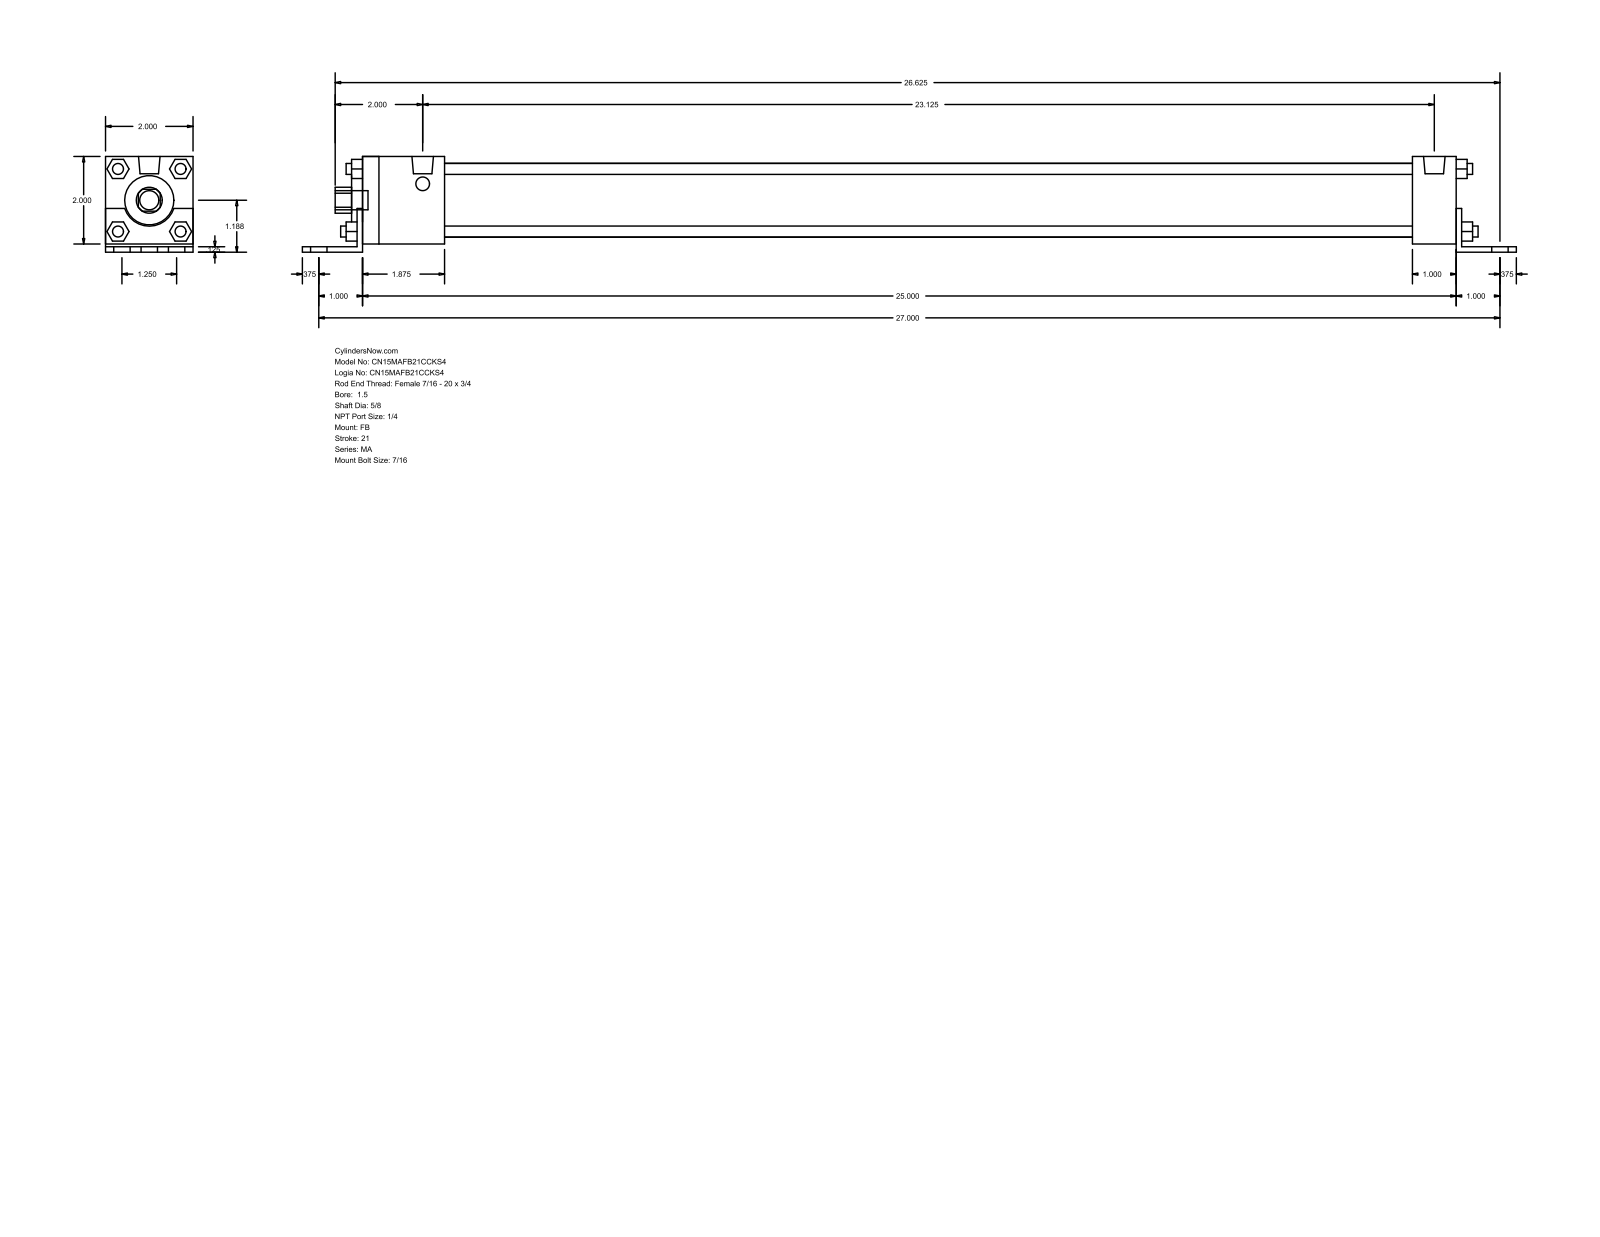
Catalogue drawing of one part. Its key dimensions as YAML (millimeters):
part_name: "MA_FB__0150_0.625"
step_written_by: "GSSL Pune (CONFIG_CONTROL_DESIGN)"
units: millimeters
bodies: {solids: 0, faces: 140, planar: 105, cylindrical: 35, other: 0}
overall_size: [704.85, 55.56, 50.8]
round_holes:
  - {diameter: 15.88, count: 1}
  - {diameter: 28.57, count: 1}
  - {diameter: 42.93, count: 1}
round_bosses_or_shafts:
  - {diameter: 11.11, count: 7}
  - {diameter: 7.94, count: 4}
  - {diameter: 6.35, count: 4}
  - {diameter: 12.49, count: 2}
partial_cylinders:
  - {radius: 7.54, count: 1}
  - {radius: 15.05, count: 1}
face_to_face_distances: [50.8, 3.17, 4.76, 55.56, 1.59, 52.39, 25.4, 641.35, 6.35, 3.18]
